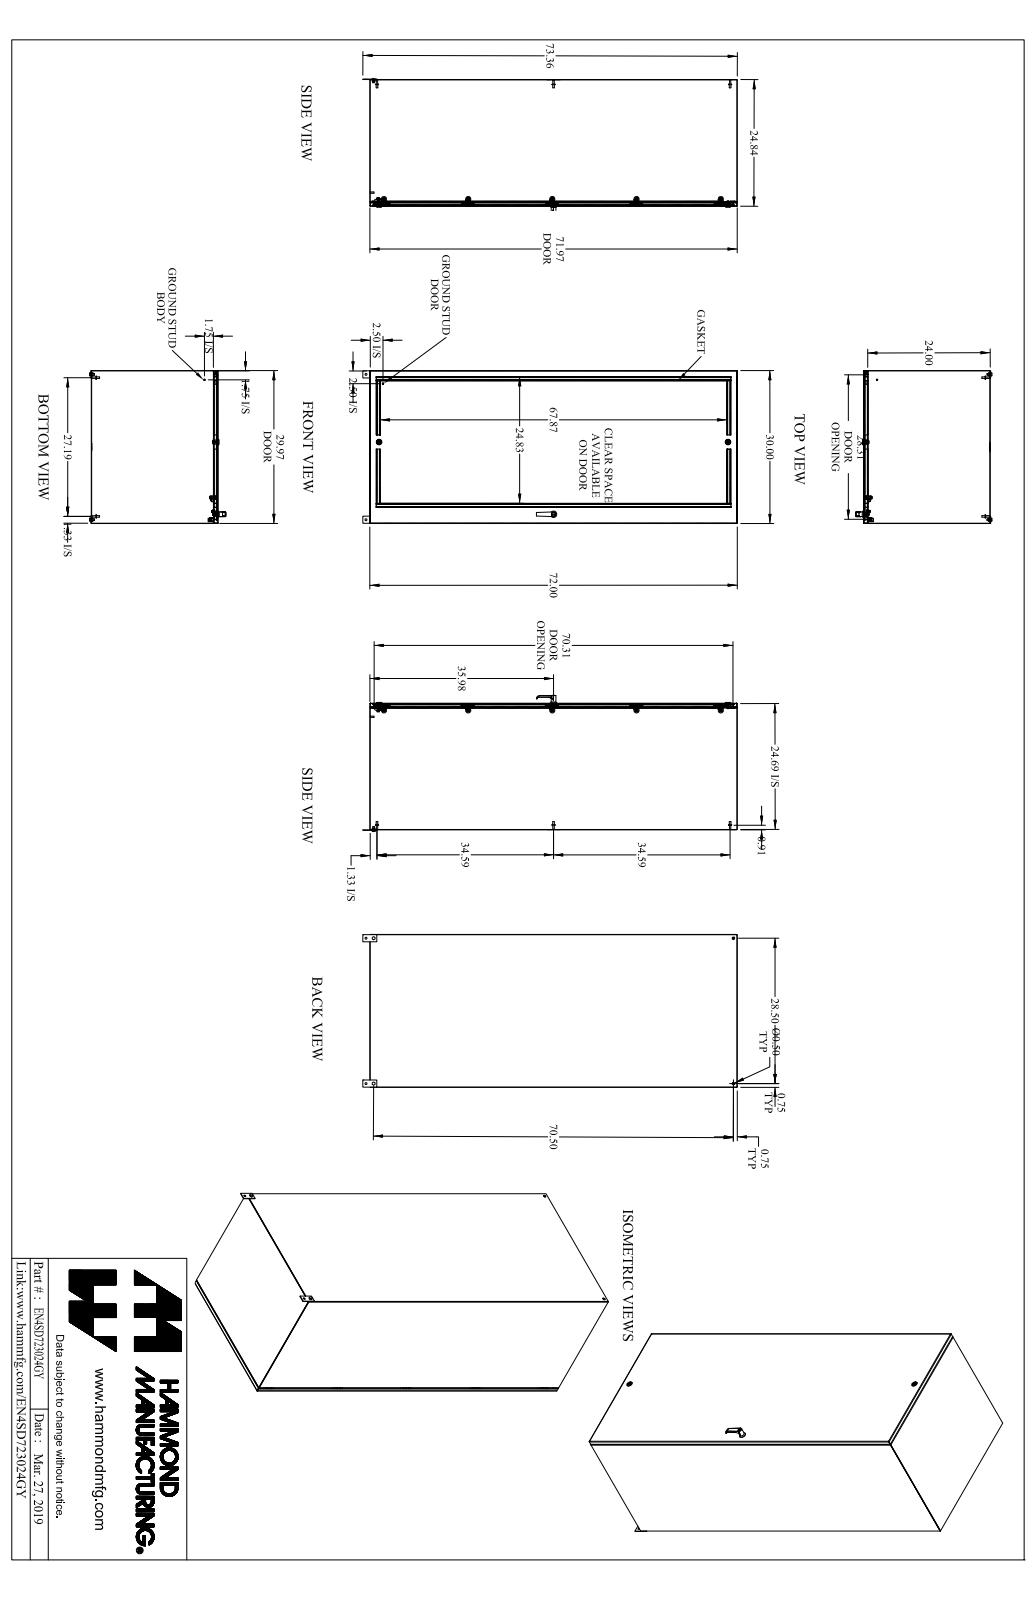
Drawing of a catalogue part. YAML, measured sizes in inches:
part_name: "EN4SD723024GY"
step_written_by: "SolidWorks 2018 (AUTOMOTIVE_DESIGN)"
units: inches
bodies: {solids: 99, faces: 2431, planar: 1163, cylindrical: 888, other: 380}
overall_size: [73.363, 30, 26.693]
volume: 749.2
surface_area: 21010
round_holes:
  - {diameter: 0.176, count: 10}
  - {diameter: 0.196, count: 6}
  - {diameter: 0.25, count: 5}
  - {diameter: 0.265, count: 5}
  - {diameter: 0.413, count: 5}
  - {diameter: 0.256, count: 4}
  - {diameter: 0.313, count: 4}
  - {diameter: 0.39, count: 4}
  - {diameter: 0.394, count: 4}
  - {diameter: 0.5, count: 4}
  - {diameter: 0.232, count: 2}
  - {diameter: 0.307, count: 2}
round_bosses_or_shafts:
  - {diameter: 0.25, count: 11}
  - {diameter: 0.375, count: 10}
  - {diameter: 0.156, count: 10}
  - {diameter: 0.625, count: 7}
  - {diameter: 0.313, count: 6}
  - {diameter: 0.27, count: 6}
  - {diameter: 1, count: 5}
  - {diameter: 0.63, count: 4}
partial_cylinders:
  - {radius: 0.043, count: 24}
  - {radius: 0.062, count: 23}
  - {radius: 0.036, count: 16}
  - {radius: 0.108, count: 16}
  - {radius: 0.03, count: 15}
  - {radius: 0.125, count: 14}
  - {radius: 0.006, count: 10}
  - {radius: 0.094, count: 10}
face_to_face_distances: [0.072, 24.765, 29.928, 24.693, 24.837, 29.856, 30, 71.928, 71.856, 72]
hole_center_spacings: [16.513, 28.5, 49.487, 0.787, 1.5, 2.507, 13.313, 14.208]
